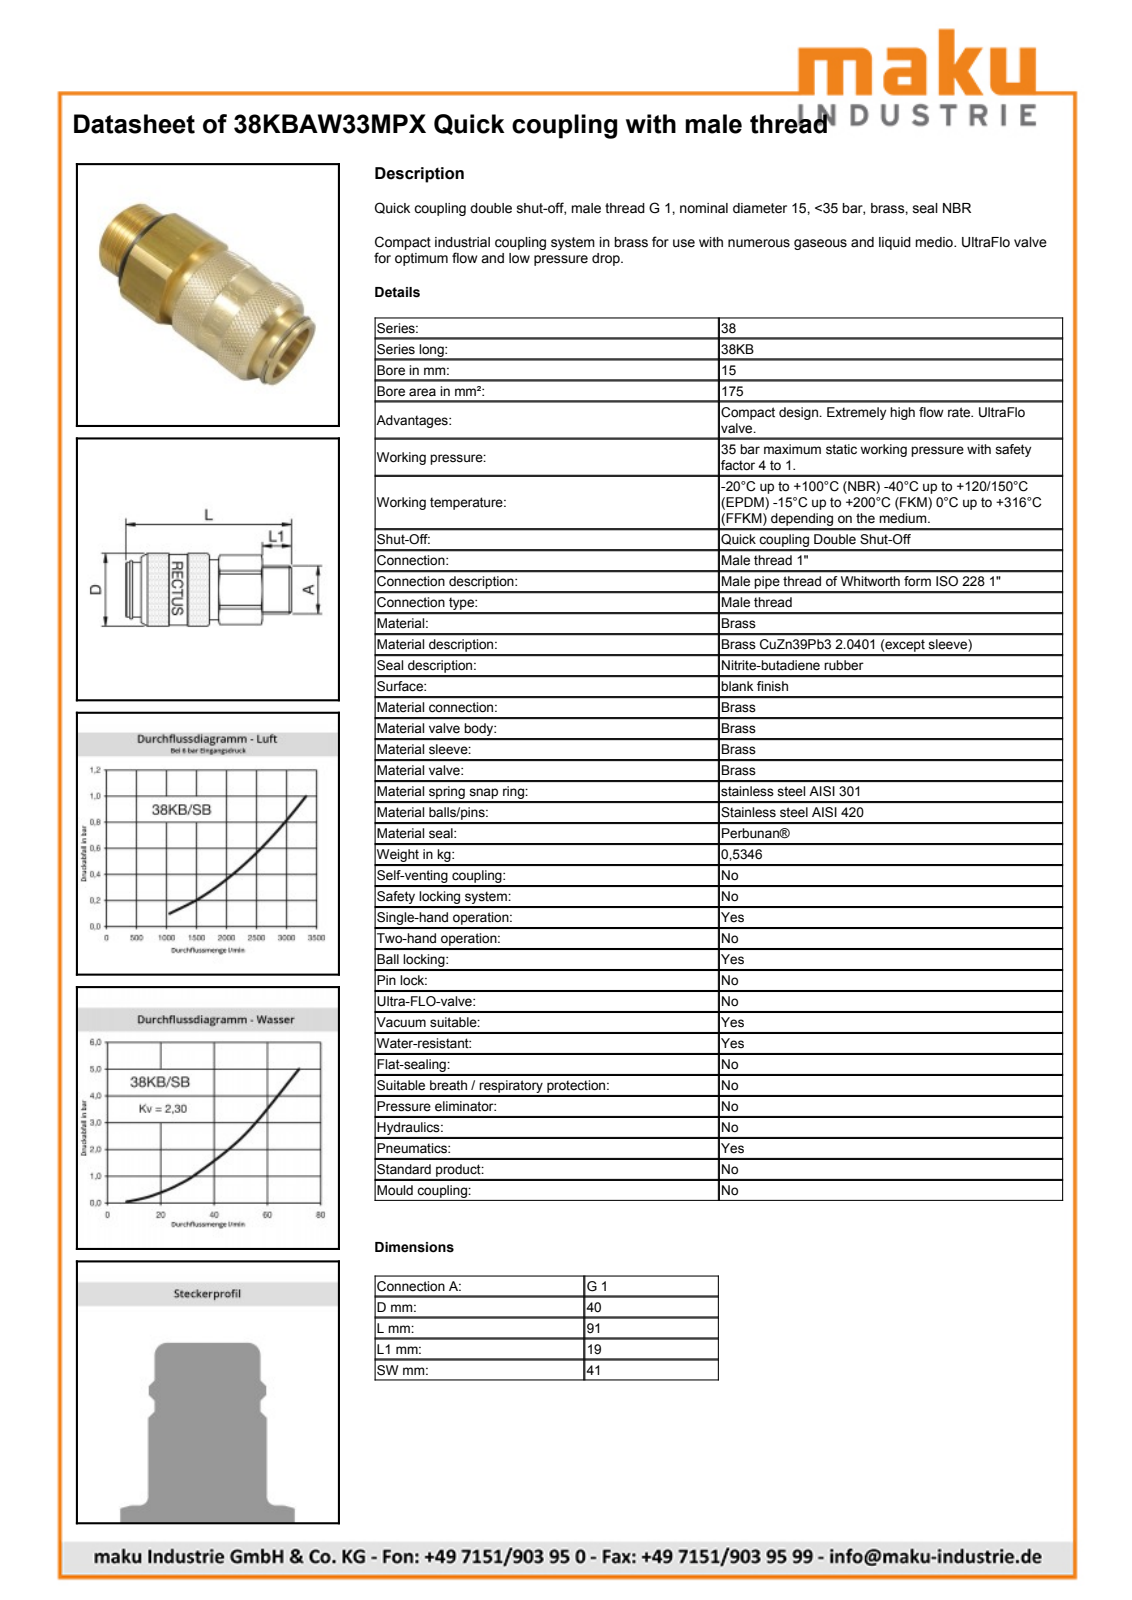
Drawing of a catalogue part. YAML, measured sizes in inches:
part_name: "D111277"
step_written_by: "Autodesk Inventor 2013 (AUTOMOTIVE_DESIGN)"
units: inches
bodies: {solids: 2, faces: 521, planar: 186, cylindrical: 76, other: 259}
overall_size: [3.486, 1.761, 1.731]
volume: 5.935
surface_area: 37.77
round_holes:
  - {diameter: 1.006, count: 1}
  - {diameter: 1.14, count: 1}
  - {diameter: 1.181, count: 1}
  - {diameter: 1.211, count: 1}
  - {diameter: 1.356, count: 1}
  - {diameter: 1.362, count: 1}
round_bosses_or_shafts:
  - {diameter: 1.575, count: 1}
  - {diameter: 1.535, count: 1}
  - {diameter: 1.339, count: 1}
  - {diameter: 1.309, count: 1}
  - {diameter: 1.122, count: 1}
  - {diameter: 1.002, count: 1}
partial_cylinders:
  - {radius: 0.764, count: 1}
  - {radius: 0.886, count: 1}
face_to_face_distances: [3.486, 2.738, 0.748, 1.911, 0.827, 1.575, 1.614, 1.613, 1.615, 0.321]
